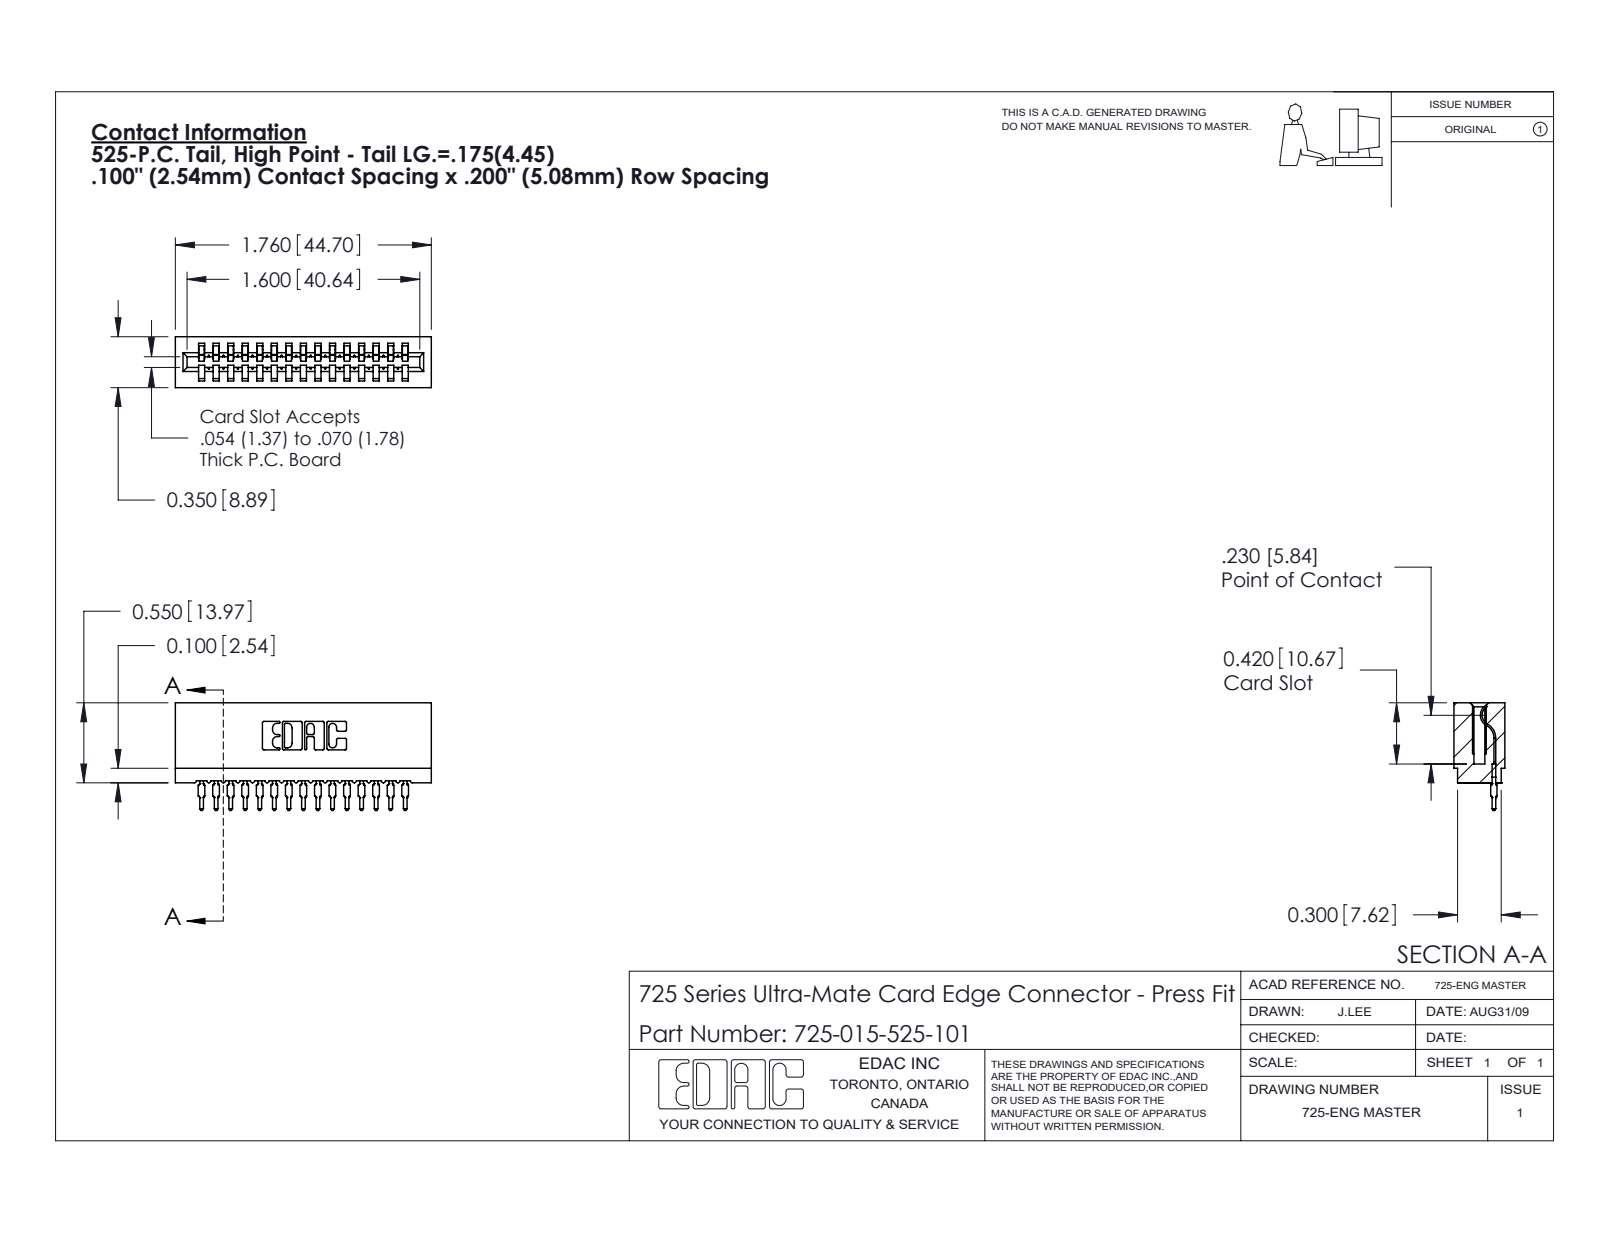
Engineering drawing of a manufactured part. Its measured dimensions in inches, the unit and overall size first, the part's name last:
Units: inches
Overall size (bounding box): 1.76 × 0.741 × 0.35
Partial cylindrical surfaces — rounded edges, fillets, slot ends (radius × count): R0.015 ×30, R0.021 ×30, R0.01 ×22, R0.007 ×6, R0.031 ×6, R0.005 ×4, R0.011 ×4, R0.026 ×3
Main face-to-face distances: 0.1, 0.2, 0.3, 0.6, 0.4, 0.5, 0.7, 0.35, 0.212, 0.138
Volume: 0.215 in³ · Surface area: 9.729 in²
Bodies: 16 solids, 1775 faces (1060 planar, 325 cylindrical, 390 other)
Part name (STEP PRODUCT): 745-292-001_525; 725-015-525-101; 725 Part_Insulator Option - 01
STEP written by: SolidWorks 2020 (CONFIG_CONTROL_DESIGN)
